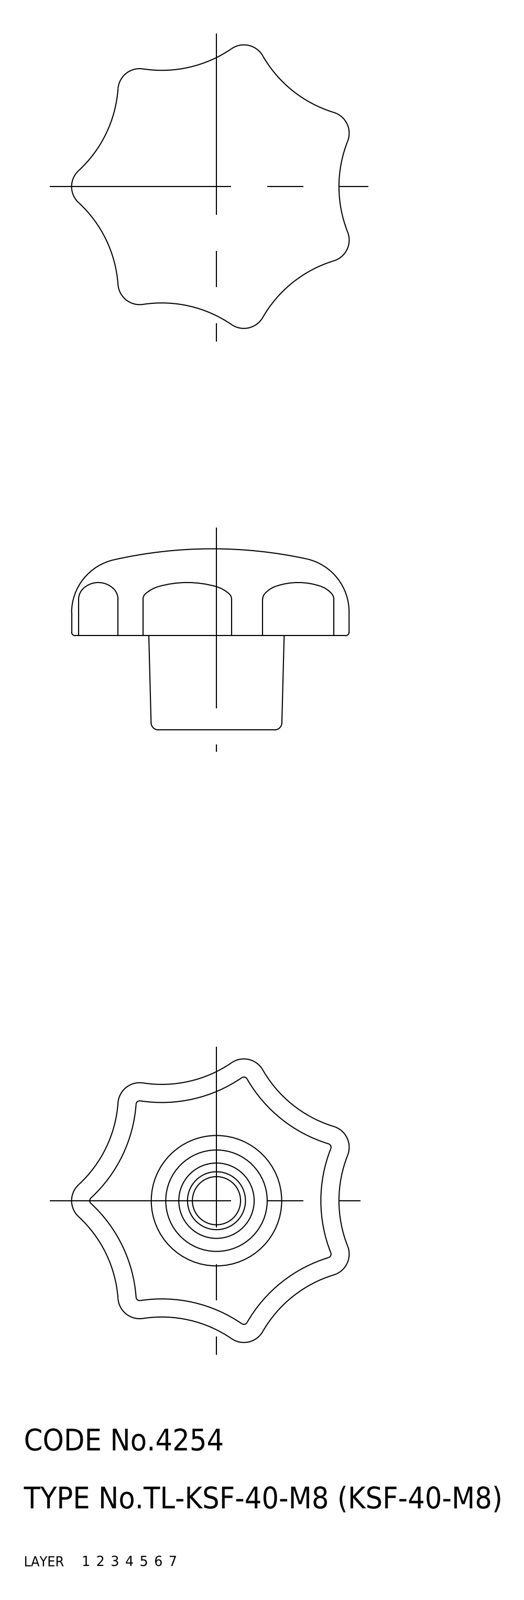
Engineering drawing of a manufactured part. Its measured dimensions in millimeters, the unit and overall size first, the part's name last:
Units: millimetres
Overall size (bounding box): 39.15 × 38.32 × 25
Volume: 9 801 mm³ · Surface area: 6 213 mm²
Bodies: 2 solids, 100 faces (0 planar, 0 cylindrical, 100 other)
Part name (STEP PRODUCT): screw; knob; KSF_40_M8_8460_36
STEP written by: CADfix (AUTOMOTIVE_DESIGN)
